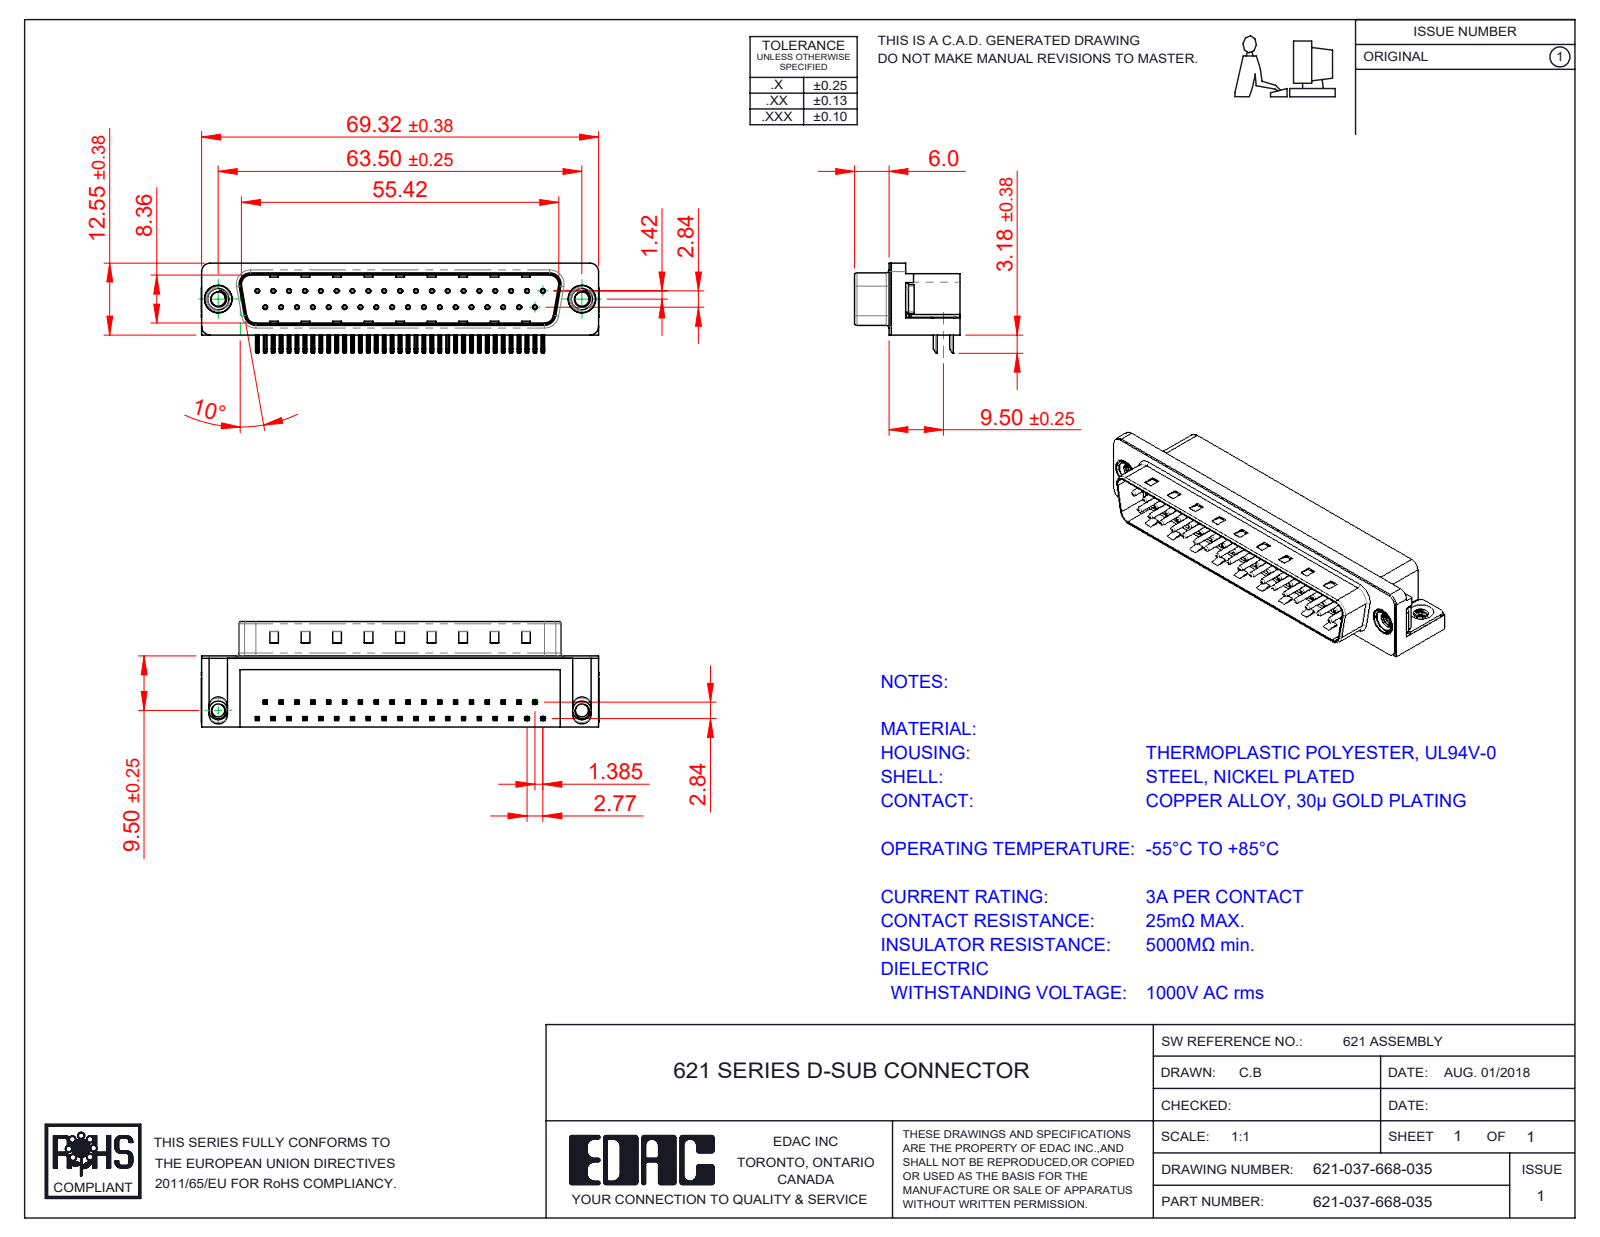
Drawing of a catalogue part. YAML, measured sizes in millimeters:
part_name: "621 Housing_37 Socket; 621 2 Prong Board Lock; 621 Shell_37 Socket; 621 Contact Bottom (+3 more)"
step_written_by: "SolidWorks 2016 (CONFIG_CONTROL_DESIGN)"
units: millimeters
bodies: {solids: 43, faces: 3239, planar: 2045, cylindrical: 927, other: 267}
overall_size: [69.4, 18.4, 16.25]
volume: 8615
surface_area: 10103
round_holes:
  - {diameter: 0.35, count: 37}
  - {diameter: 0.8, count: 37}
  - {diameter: 2.5, count: 2}
  - {diameter: 4, count: 2}
  - {diameter: 4.8, count: 2}
  - {diameter: 5, count: 2}
round_bosses_or_shafts:
  - {diameter: 0.75, count: 37}
  - {diameter: 4.9, count: 2}
  - {diameter: 4.75, count: 2}
  - {diameter: 3.9, count: 2}
partial_cylinders:
  - {radius: 0.25, count: 156}
  - {radius: 0.12, count: 74}
  - {radius: 1, count: 16}
  - {radius: 0.5, count: 14}
  - {radius: 1.6, count: 8}
  - {radius: 1.5, count: 7}
  - {radius: 0.32, count: 4}
  - {radius: 0.9, count: 4}
face_to_face_distances: [0.4, 12, 10.35, 8.76, 1.7, 2.1, 10.46, 10.86, 9, 12.4]
hole_center_spacings: [3.16, 2.77, 5.54, 8.31, 11.08, 13.85, 19.39, 22.16]
